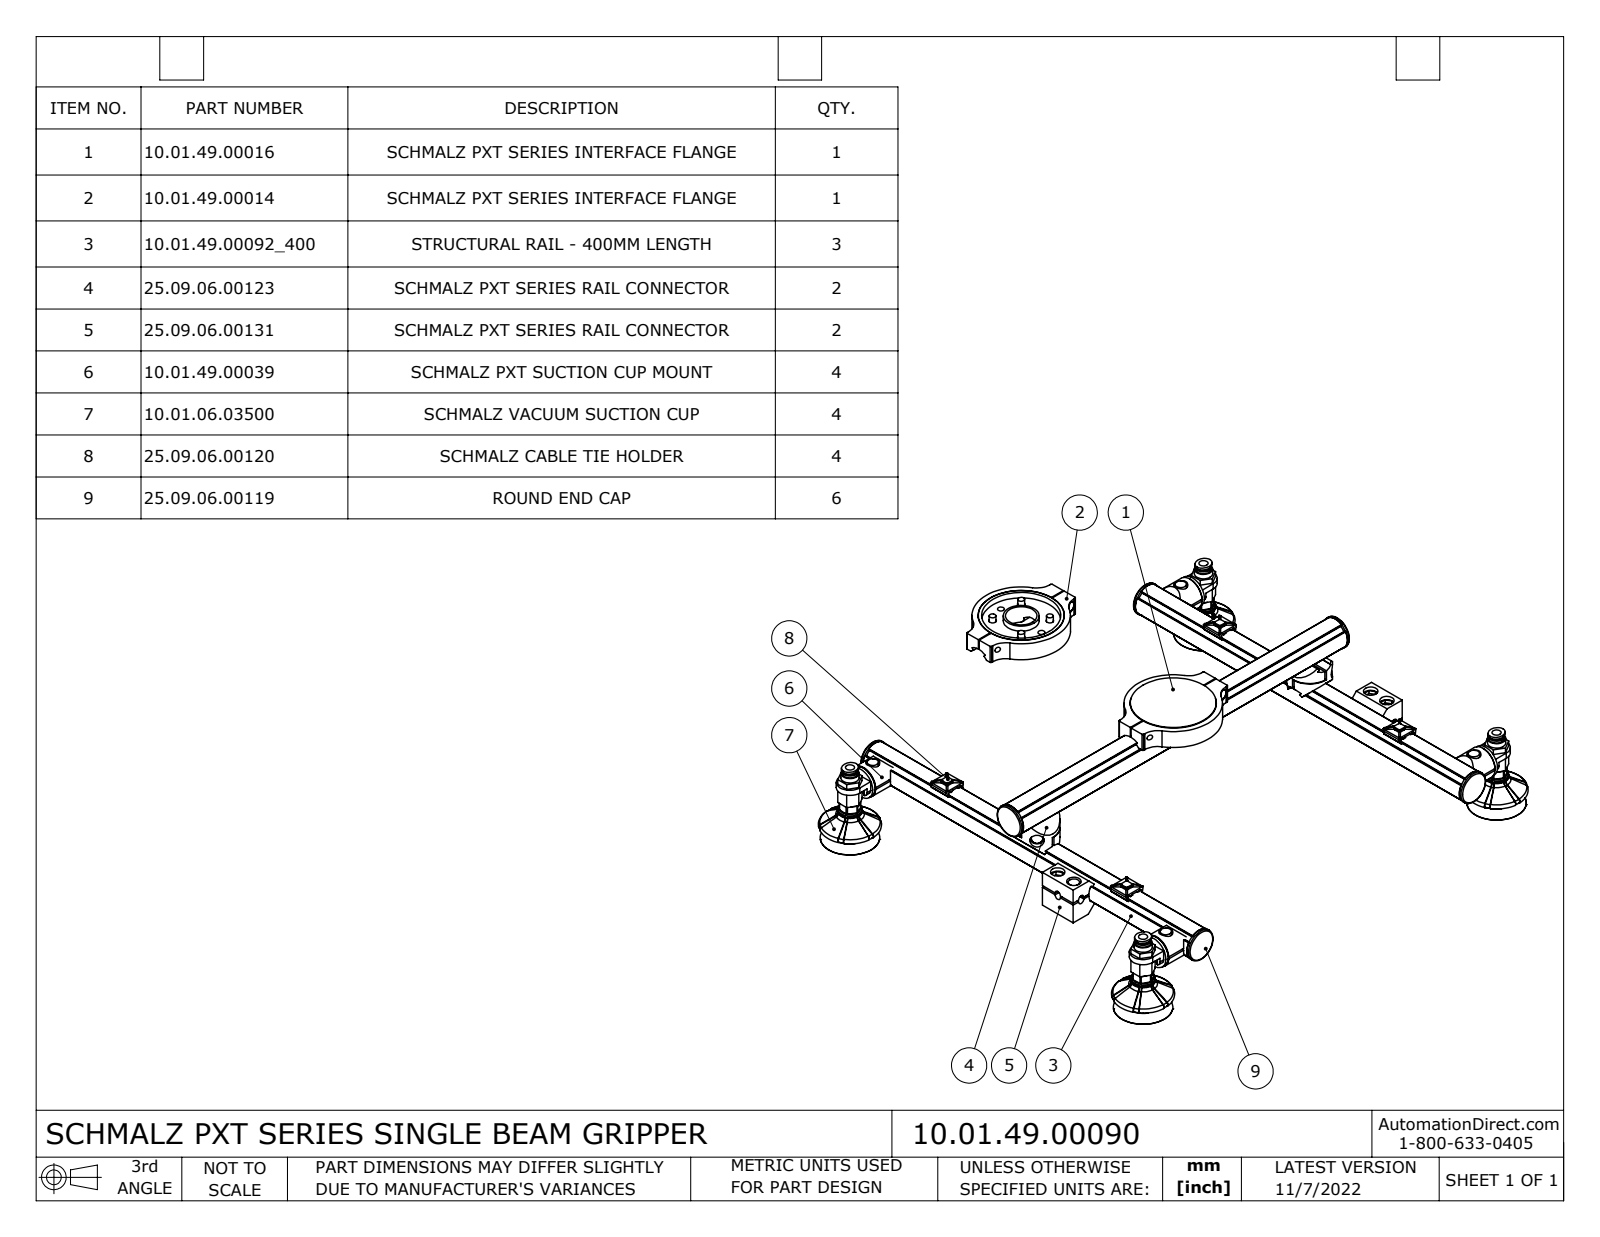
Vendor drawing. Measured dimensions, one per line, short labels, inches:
name: 10.01.49.00014; 25.09.06.00119; 25.09.06.00123; 10.01.49.00090 (+6 more)
written by: SolidWorks 2021 (CONFIG_CONTROL_DESIGN)
unit: in
bodies: 89 solids, 3169 faces (1398 planar, 1151 cylindrical, 620 other)
size: 19.358 × 17.295 × 4.961
volume: 45.36 in³; area: 770 in²
holes: 14× ⌀0.197, 8× ⌀0.26, 8× ⌀0.433, 6× ⌀0.24, 4× ⌀0.256, 4× ⌀0.276, 4× ⌀0.315, 4× ⌀0.351, 4× ⌀0.394, 4× ⌀0.402, 4× ⌀0.465, 4× ⌀0.488
bosses: 14× ⌀0.394, 14× ⌀0.236, 5× ⌀1.181, 4× ⌀0.827, 4× ⌀0.669, 4× ⌀0.63, 4× ⌀0.551, 4× ⌀0.545
rounds: 88× R0.012, 48× R0.016, 28× R0.039, 24× R0.02, 24× R0.059, 10× R0.492, 8× R0.02, 8× R0.126
face distances: 0.244, 0.118, 0.059, 9.366, 4.272, 0.142, 4.961, 0.689, 0.122, 0.22
hole spacings: 0.984, 14.248, 0.754, 1.106, 1.392, 1.819, 10.334, 11.162
